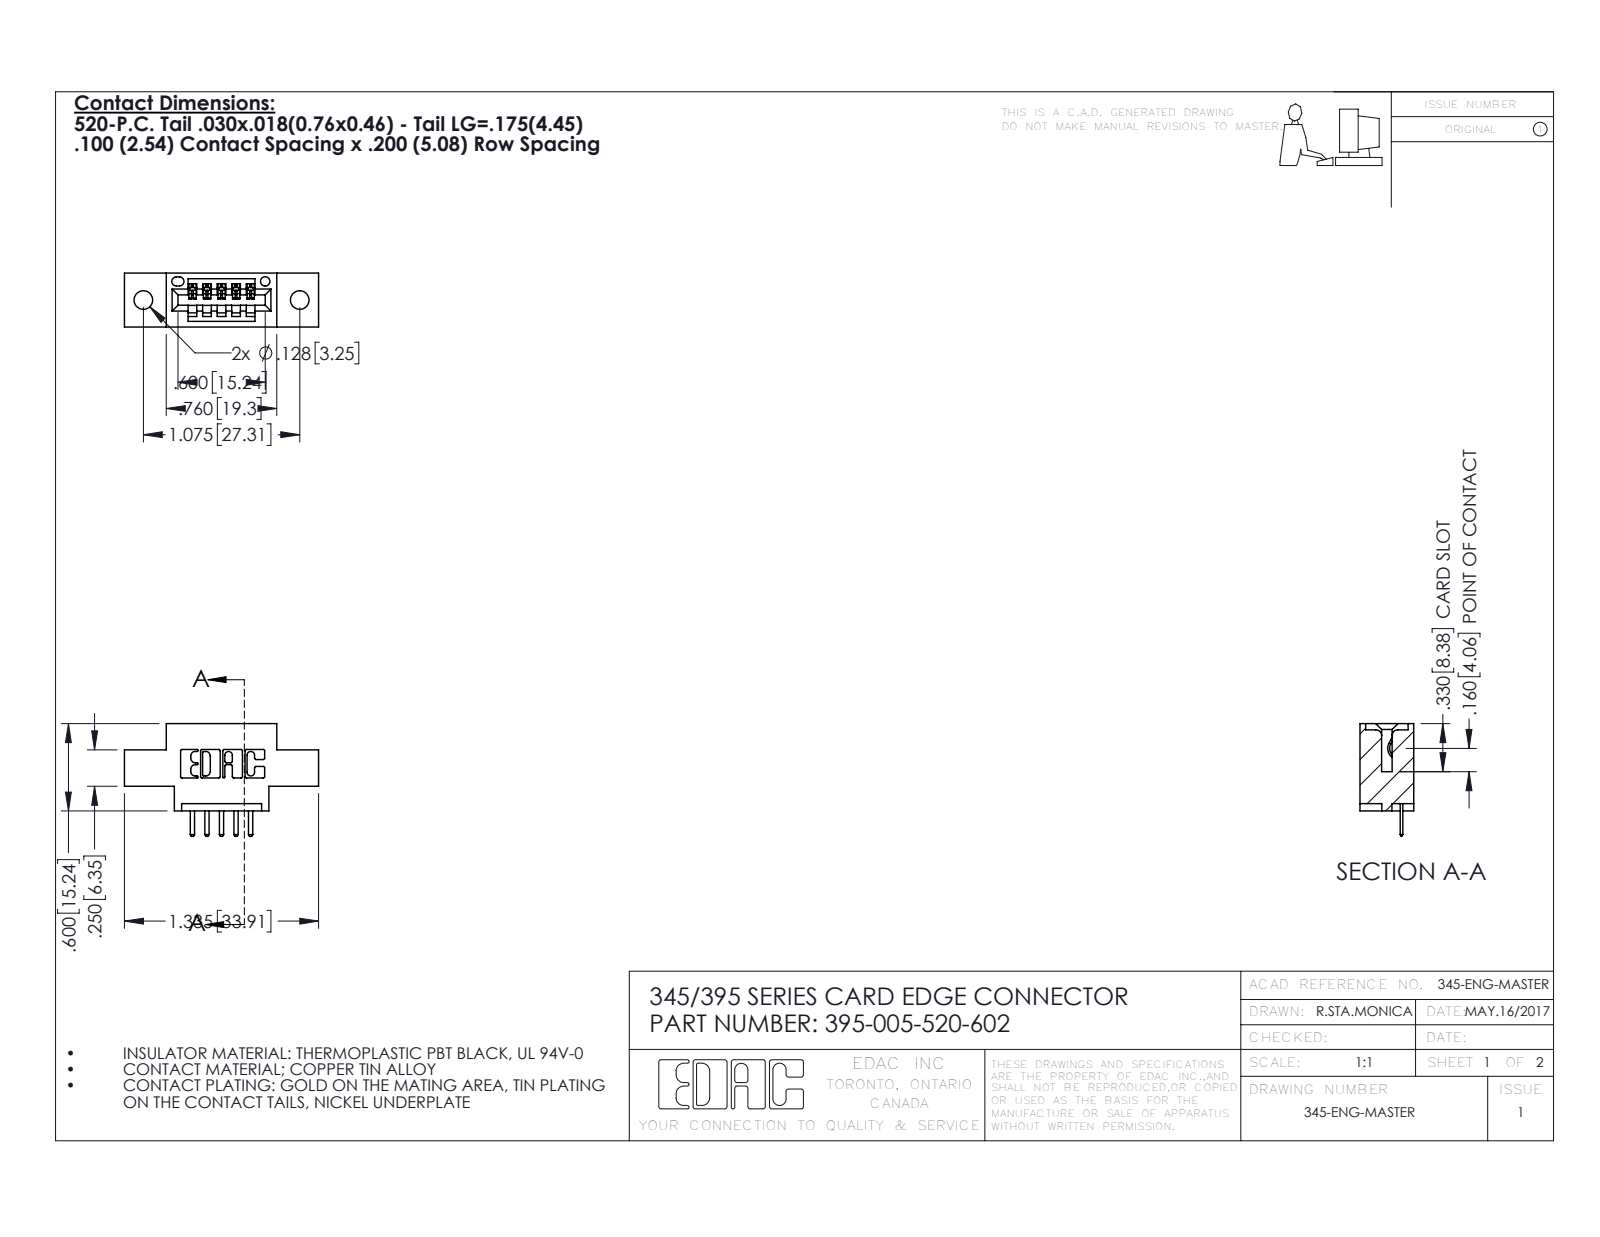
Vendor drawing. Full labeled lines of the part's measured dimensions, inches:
Part name (STEP PRODUCT): 345-292-001_345-293-120; 395-005-520-602; 345 Part_0.170 Offset - 0.128 Dia
STEP written by: SolidWorks 2016 (CONFIG_CONTROL_DESIGN)
Units: inches
Bodies: 6 solids, 440 faces (294 planar, 146 cylindrical, 0 other)
Overall size (bounding box): 1.335 × 0.775 × 0.37
Volume: 0.168 in³ · Surface area: 4.594 in²
Round holes (diameter × count): ⌀0.128 ×2, ⌀0.064 ×1
Partial cylindrical surfaces — rounded edges, fillets, slot ends (radius × count): R0.01 ×22, R0.01 ×12, R0.006 ×10, R0.007 ×6, R0.031 ×6, R0.026 ×3, R0.031 ×2, R0.04 ×2
Main face-to-face distances: 0.37, 0.2, 0.1, 0.298, 0.072, 0.25, 0.025, 0.06, 0.55, 0.15
Hole centre spacings: 0.27, 0.847, 1.075
